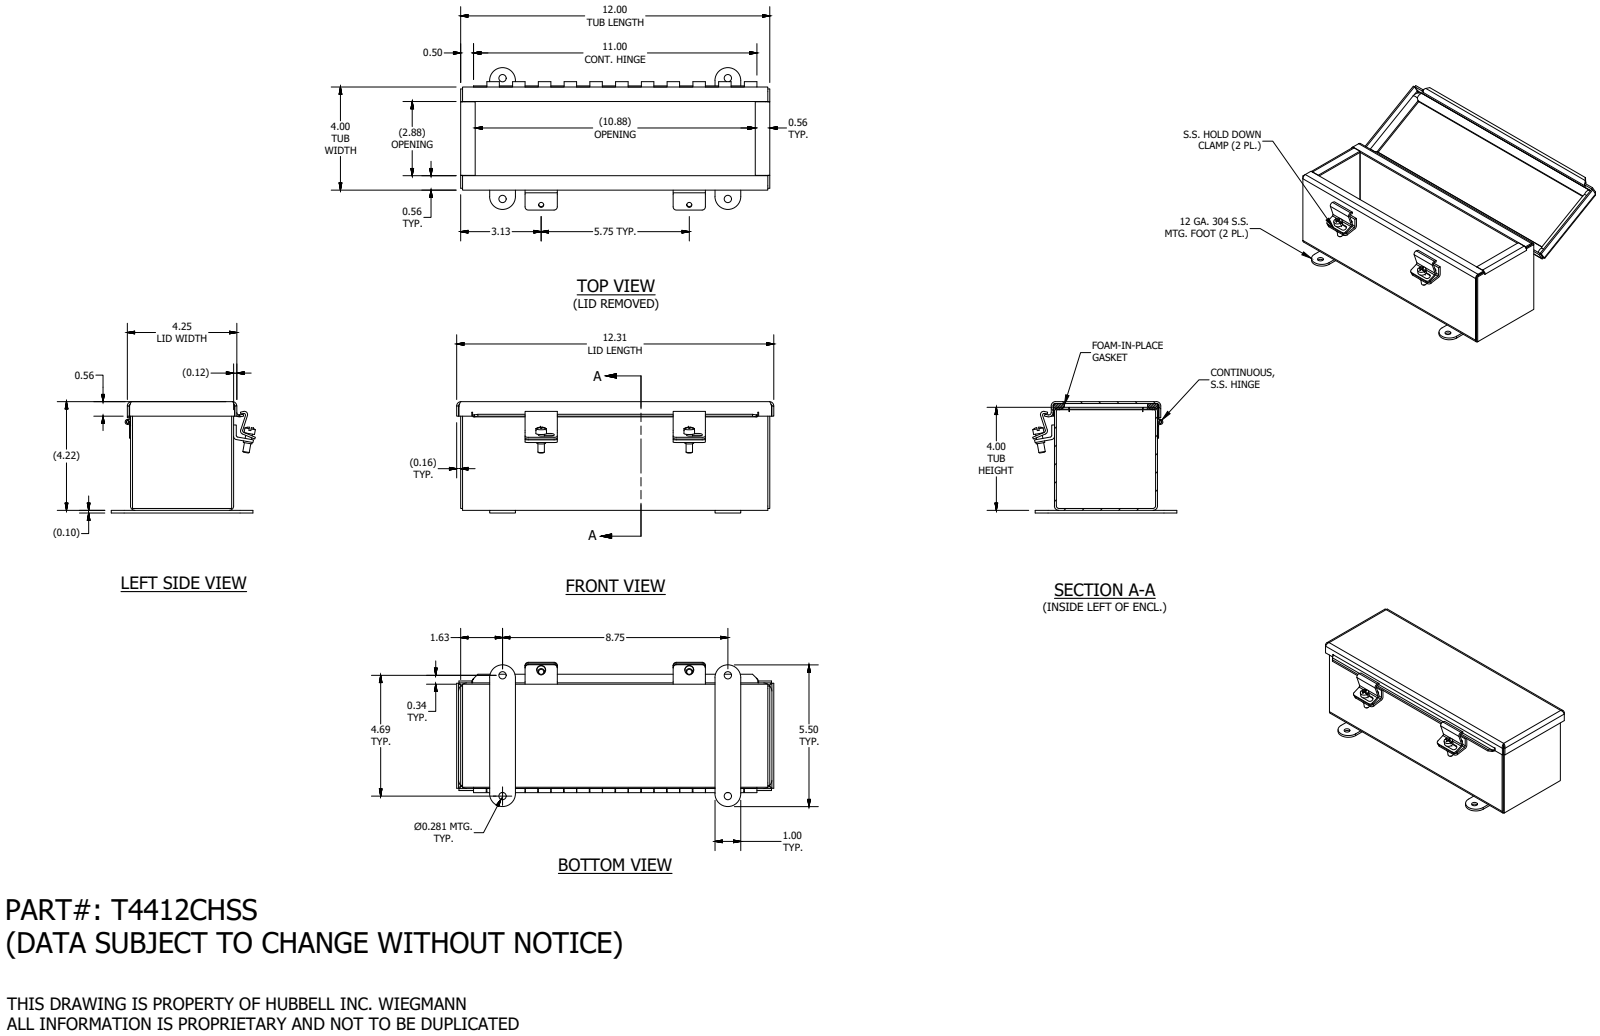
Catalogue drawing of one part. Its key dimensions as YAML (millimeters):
part_name: "T4412CHSS"
step_written_by: "SolidWorks 2019 (AUTOMOTIVE_DESIGN)"
units: millimeters
bodies: {solids: 16, faces: 406, planar: 245, cylindrical: 129, other: 32}
overall_size: [312.8, 142.2, 109.8]
volume: 390300
surface_area: 405100
round_holes:
  - {diameter: 2.8, count: 4}
  - {diameter: 7.1, count: 4}
  - {diameter: 5, count: 2}
  - {diameter: 2.9, count: 1}
round_bosses_or_shafts:
  - {diameter: 10.4, count: 2}
  - {diameter: 8.7, count: 2}
  - {diameter: 6.4, count: 2}
  - {diameter: 5.1, count: 1}
  - {diameter: 2.5, count: 1}
partial_cylinders:
  - {radius: 2.4, count: 11}
  - {radius: 4.3, count: 11}
  - {radius: 2.2, count: 8}
  - {radius: 3.2, count: 8}
  - {radius: 3.4, count: 4}
  - {radius: 6.1, count: 4}
  - {radius: 12.7, count: 4}
  - {radius: 1.6, count: 3}
face_to_face_distances: [1.9, 99.7, 105.3, 101.6, 97.8, 107.1, 103.4, 302.9, 5.5, 102.9]
hole_center_spacings: [146.1, 19.1, 119, 222.3, 252.1, 127, 165.1]
